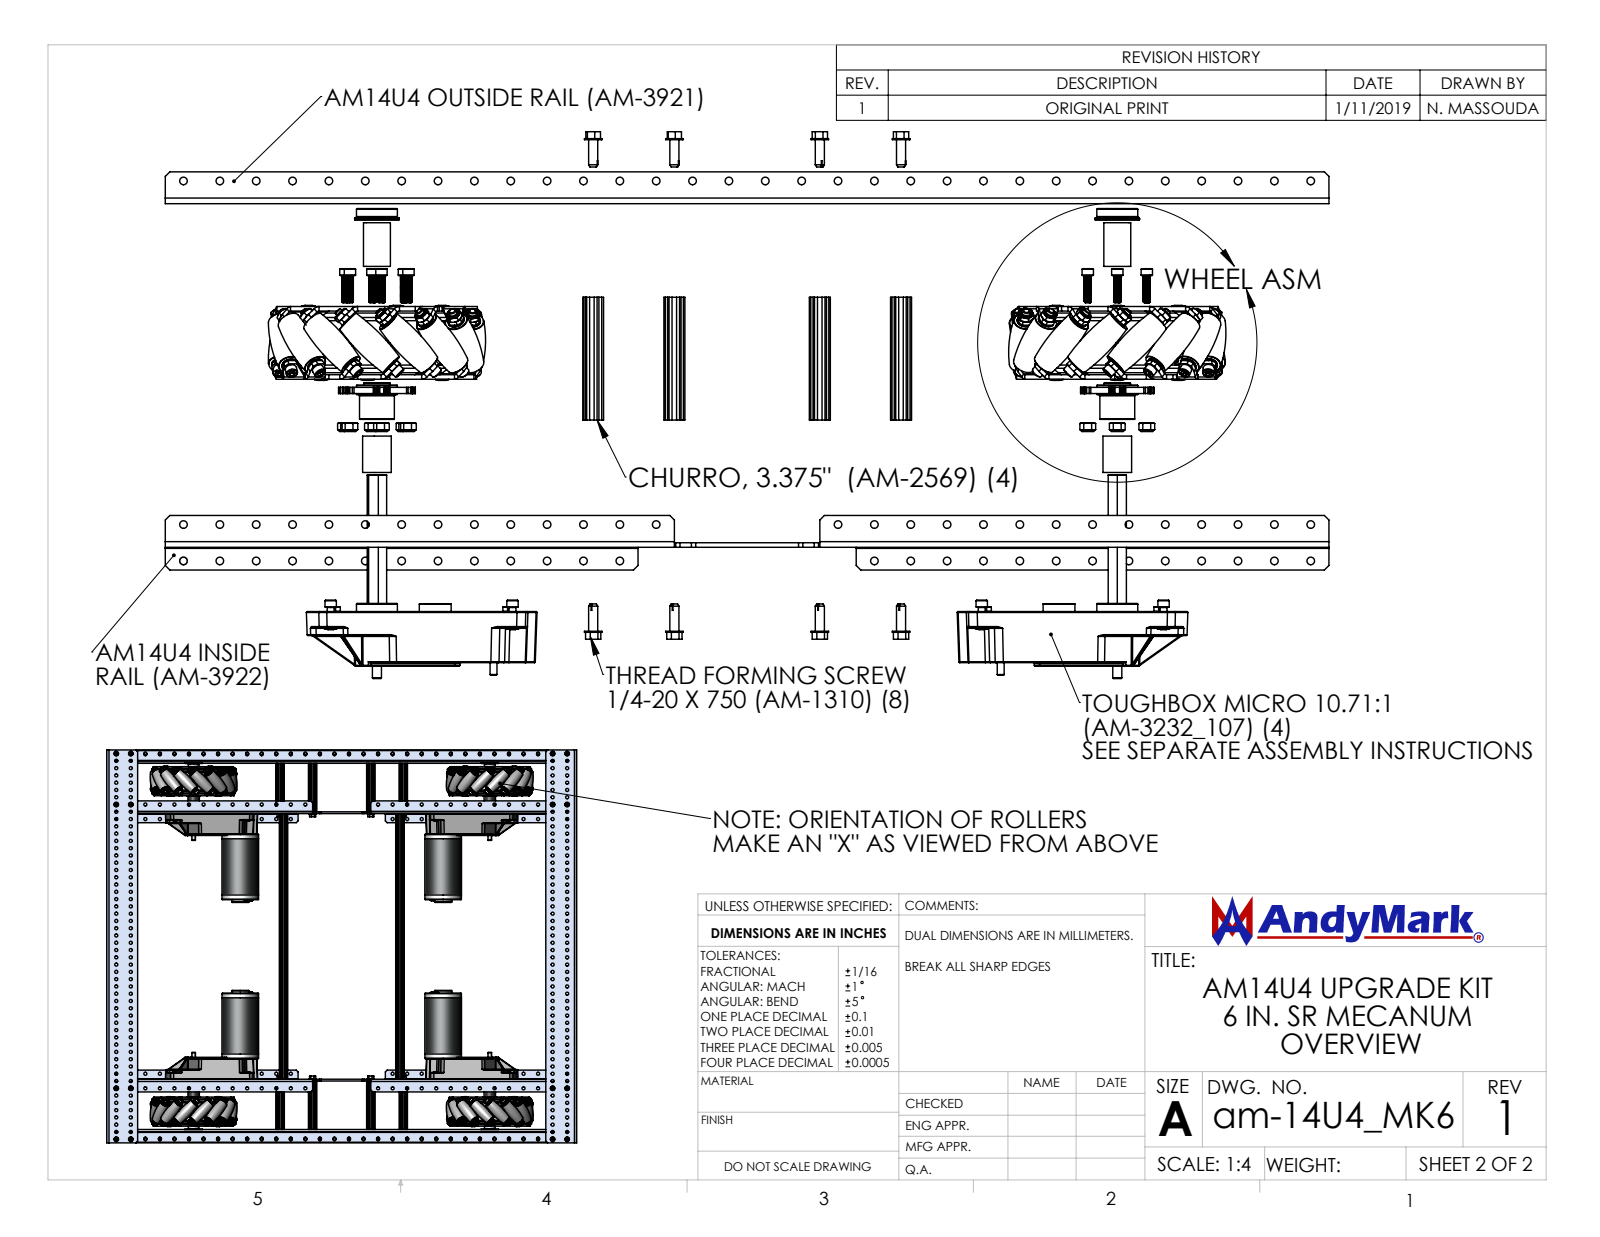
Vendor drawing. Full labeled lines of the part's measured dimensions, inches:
Part name (STEP PRODUCT): am-0676a Left Plate HD; 8mm_spring_clip am-0033; am-3479Ra 6 SR Mecanum Left with Standoffs for AM14U Family; am-3698_skin TPU v2 (+8 more)
STEP written by: SolidWorks 2021 (AUTOMOTIVE_DESIGN)
Units: inches
Bodies: 886 solids, 34292 faces (8282 planar, 13386 cylindrical, 12624 other)
Overall size (bounding box): 32.31 × 27 × 5.979
Volume: 344 in³ · Surface area: 4 872 in²
Round holes (diameter × count): ⌀0.164 ×576, ⌀0.21 ×364, ⌀0.203 ×132, ⌀0.25 ×120, ⌀0.313 ×118, ⌀0.19 ×106, ⌀0.161 ×100, ⌀0.239 ×72, ⌀0.192 ×60, ⌀0.256 ×60, ⌀0.201 ×42, ⌀0.266 ×35
Round bosses / shafts (diameter × count): ⌀0.313 ×122, ⌀0.19 ×70, ⌀0.25 ×42, ⌀0.187 ×18, ⌀0.361 ×12, ⌀0.309 ×12, ⌀0.34 ×8, ⌀0.48 ×6
Partial cylindrical surfaces — rounded edges, fillets, slot ends (radius × count): R0.5 ×400, R0.025 ×386, R0.45 ×360, R0.19 ×152, R0.215 ×132, R0.082 ×124, R0.09 ×120, R0.015 ×96
Main face-to-face distances: 0.125, 3.5, 0.135, 0.125, 3.07, 0.26, 21.875, 22, 21.75, 21.875
Hole centre spacings: 0.015, 0.015, 2, 0.02, 4, 1, 6, 8
